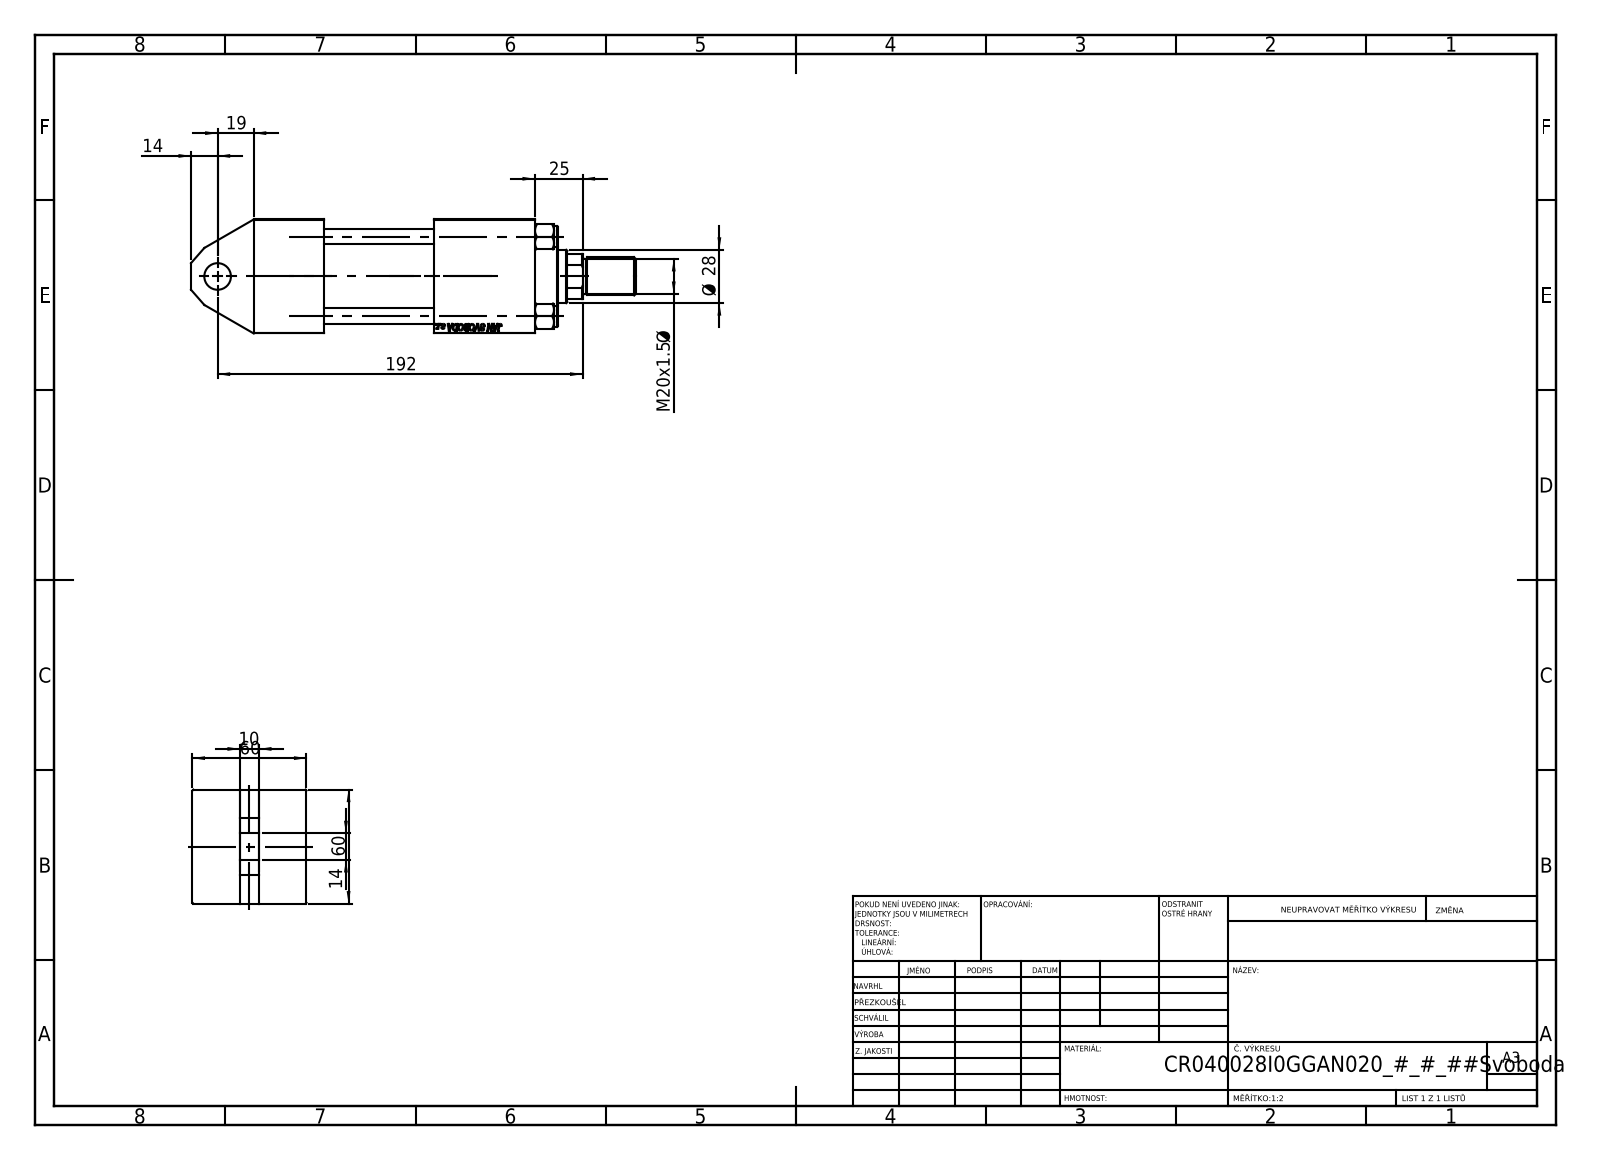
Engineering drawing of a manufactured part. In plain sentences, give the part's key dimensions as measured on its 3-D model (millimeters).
The part is named "V215CR_I_Body; V215_VC_A; ROD_END_AH; NUT_M5_I (+2 more)". Its 3-D file was written by "SolidWorks 2019 (CONFIG_CONTROL_DESIGN)". It is 12 solids with 1092 faces: 506 planar, 84 cylindrical and 502 other. Overall it measures 234 by 60 by 60 millimeters. Its volume is 448 587 cubic millimeters and its surface area 118 117 square millimeters. Round holes: 4 of diameter 8, 2 of diameter 7, 2 of diameter 16.66, 2 of diameter 24, 1 of diameter 14, 1 of diameter 18.5, 1 of diameter 28, 1 of diameter 31, 1 of diameter 40, 1 of diameter 45. Round bosses or shafts: 4 of diameter 11, 1 of diameter 46, 1 of diameter 42, 1 of diameter 20, 1 of diameter 18. Partial cylindrical surfaces (rounded edges, fillets, slot ends): 1 of radius 13.5. The main face-to-face distances are 60, 37, 25, 53, 35, 58, 95, 148, 111, 119.3. The hole center spacings are 29.49, 41.7, 58.97, 92.5.
